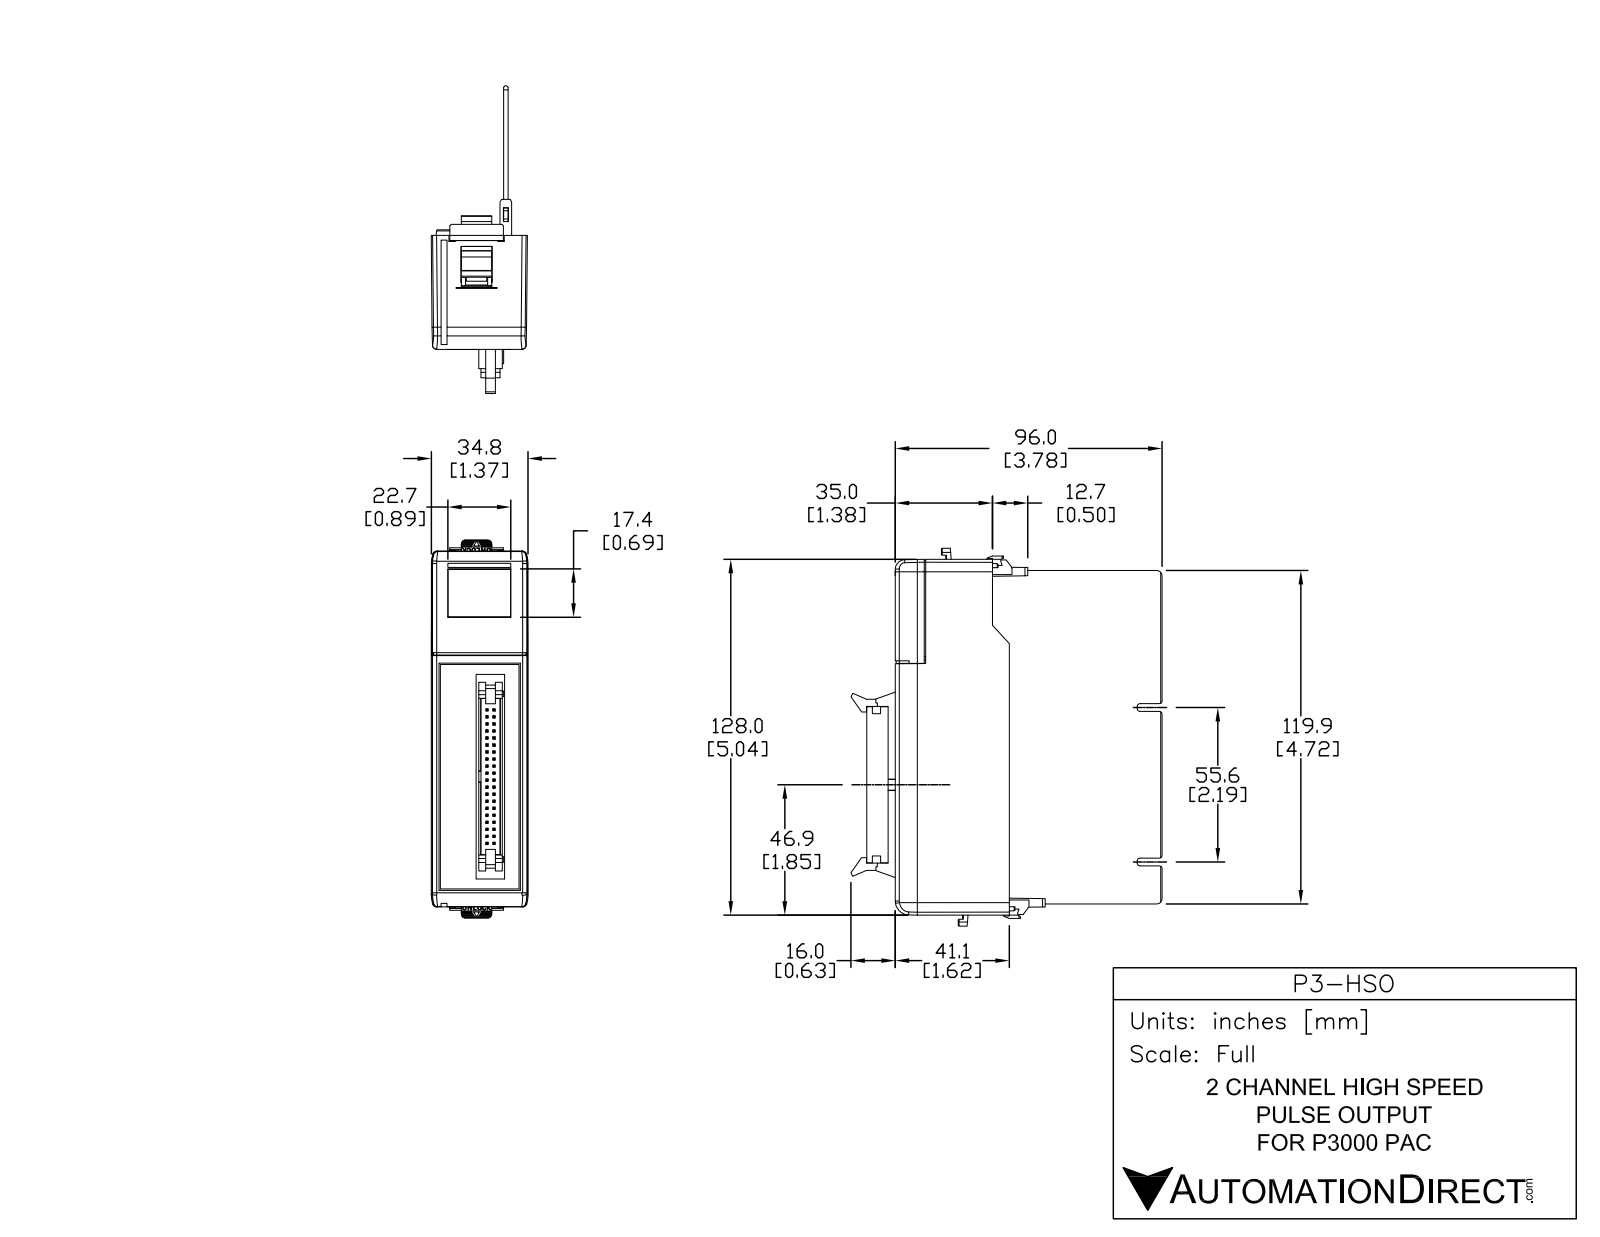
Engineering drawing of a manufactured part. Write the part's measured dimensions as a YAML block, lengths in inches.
part_name: "P3-HSO"
step_written_by: "SolidWorks 2012 (AUTOMOTIVE_DESIGN)"
units: inches
bodies: {solids: 1, faces: 1496, planar: 1371, cylindrical: 52, other: 73}
overall_size: [5.358, 4.405, 1.37]
volume: 11.62
surface_area: 68.62
partial_cylinders:
  - {radius: 0.039, count: 16}
  - {radius: 0.012, count: 10}
  - {radius: 0.059, count: 6}
  - {radius: 0.004, count: 2}
  - {radius: 0.02, count: 2}
  - {radius: 0.045, count: 2}
  - {radius: 0.047, count: 2}
  - {radius: 0.079, count: 2}
face_to_face_distances: [0.063, 1.623, 0.051, 0.114, 0.24, 1.383, 0.323, 0.303, 0.272, 0.386]
